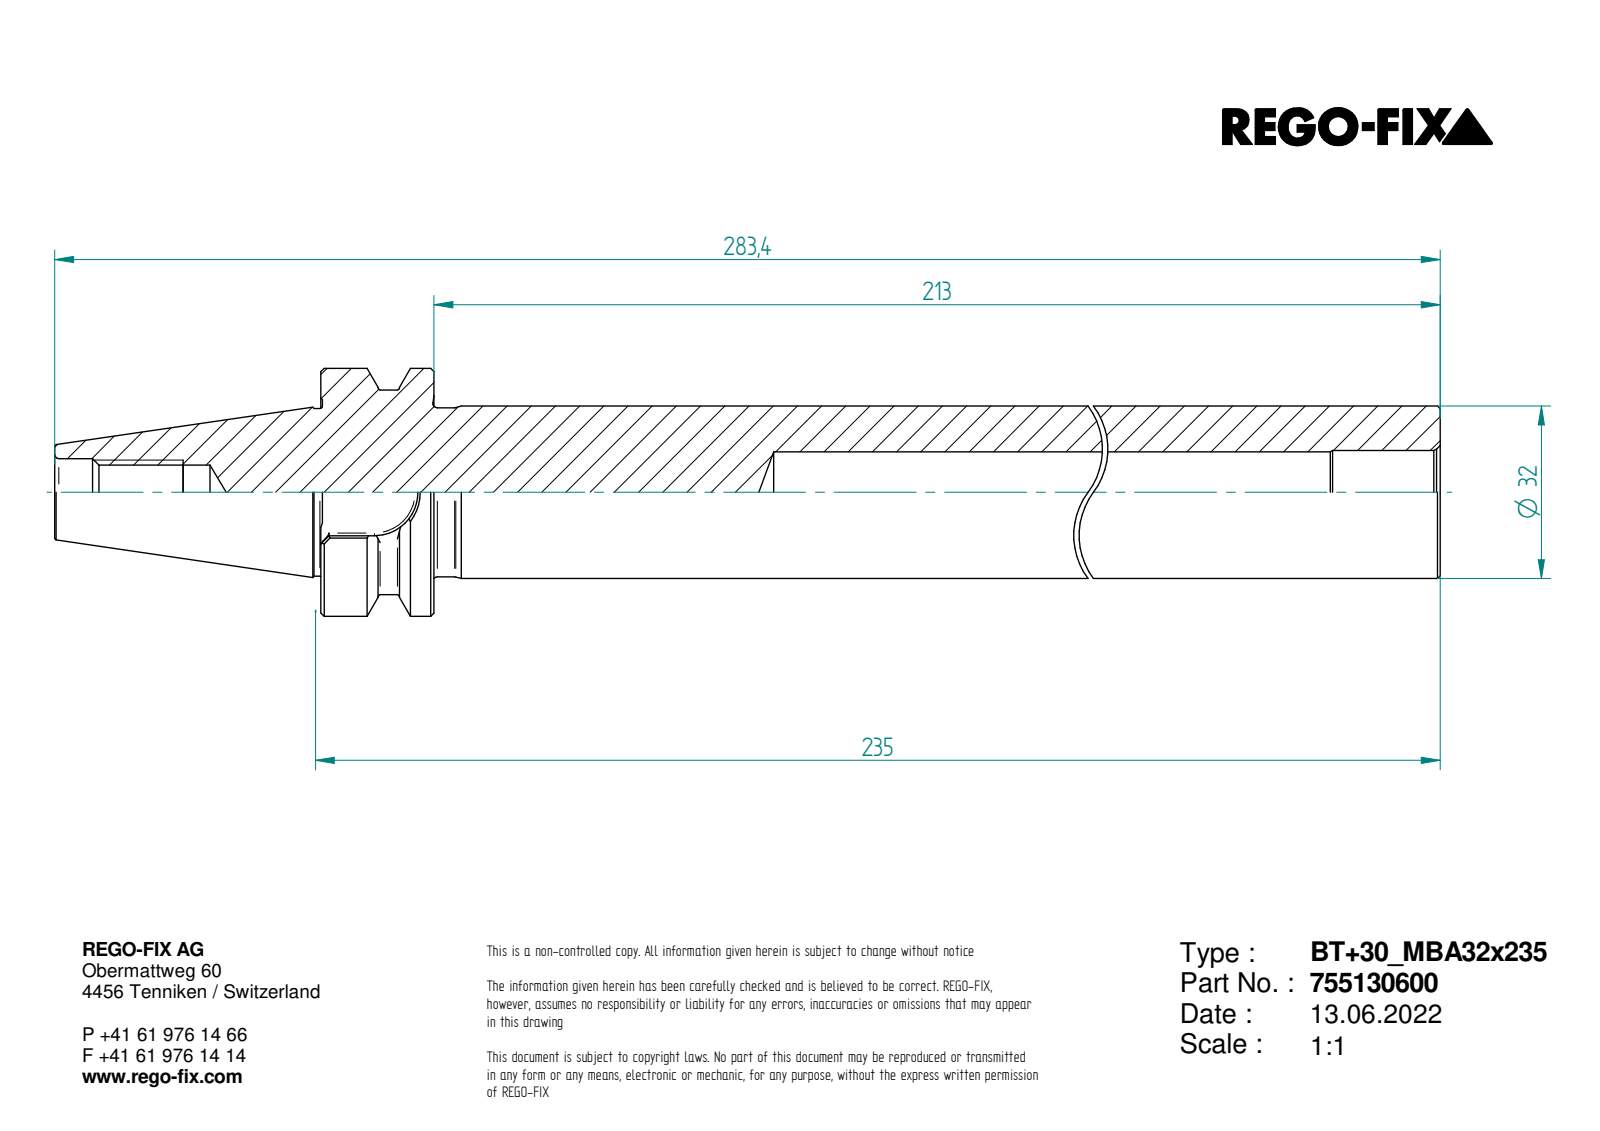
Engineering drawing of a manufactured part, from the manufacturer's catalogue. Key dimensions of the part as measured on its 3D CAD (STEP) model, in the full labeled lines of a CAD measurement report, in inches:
Part name (STEP PRODUCT): 0026161
STEP written by: ST-DEVELOPER v16.7 (AUTOMOTIVE_DESIGN)
Units: inches
Bodies: 1 solid, 93 faces (32 planar, 19 cylindrical, 42 other)
Overall size (bounding box): 11.157 × 1.811 × 1.811
Volume: 11.91 in³ · Surface area: 61.3 in²
Round holes (diameter × count): ⌀0.397 ×1, ⌀0.398 ×1, ⌀0.492 ×1, ⌀0.591 ×1, ⌀0.61 ×1
Round bosses / shafts (diameter × count): ⌀1.811 ×1, ⌀1.26 ×1, ⌀1.236 ×1, ⌀1.226 ×1
Partial cylindrical surfaces — rounded edges, fillets, slot ends (radius × count): R0.02 ×4, R0.317 ×1, R0.748 ×1
Main face-to-face distances: 8.386, 0.827, 9.213, 1.28, 0.815, 9.201, 0.634, 1.945, 1.957, 2.772
